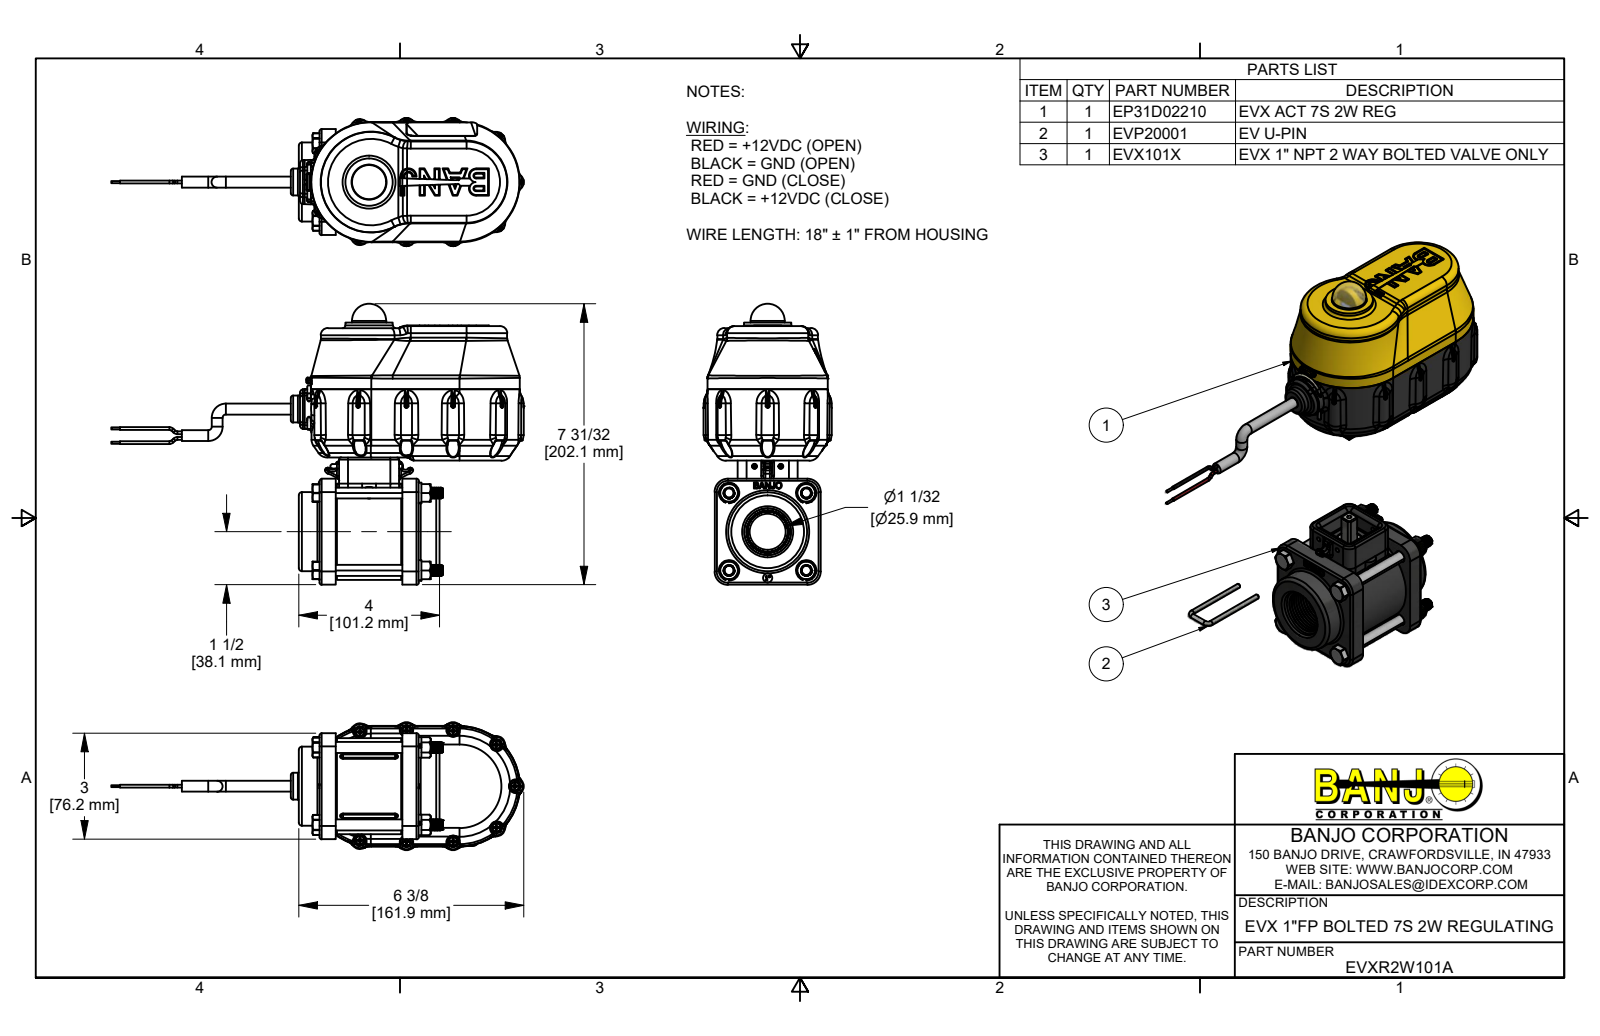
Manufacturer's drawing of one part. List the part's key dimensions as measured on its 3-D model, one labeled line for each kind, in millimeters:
Part name (STEP PRODUCT): EVXR2W101A; EVP20001; EVX101X; MEVX10254A (+8 more)
STEP written by: Autodesk Inventor 2019 (AUTOMOTIVE_DESIGN)
Units: millimetres
Bodies: 95 solids, 12807 faces (3636 planar, 3423 cylindrical, 5748 other)
Overall size (bounding box): 984.8 × 202.1 × 92.2
Volume: 822 600 mm³ · Surface area: 477 700 mm²
Round holes (diameter × count): ⌀3.8 ×13, ⌀2.4 ×11, ⌀2.7 ×4, ⌀3.2 ×4, ⌀3.4 ×4, ⌀3.5 ×4, ⌀4.3 ×4, ⌀6.4 ×4, ⌀8.2 ×4, ⌀8.9 ×4, ⌀25.9 ×3, ⌀2.3 ×2
Round bosses / shafts (diameter × count): ⌀6.8 ×60, ⌀6.4 ×17, ⌀3.6 ×11, ⌀2.7 ×11, ⌀2.2 ×11, ⌀2 ×10, ⌀8 ×5, ⌀14.8 ×4
Partial cylindrical surfaces — rounded edges, fillets, slot ends (radius × count): R1 ×147, R0.5 ×83, R1.5 ×62, R0.3 ×56, R0.1 ×41, R0.8 ×32, R2 ×28, R2.5 ×22
Main face-to-face distances: 2.5, 65.2, 42.8, 62.6, 19.8, 1.4, 11.7, 3.2, 4.2, 22.4
Hole centre spacings: 55.7, 26.6, 32.6, 39.4, 42.2, 48, 80.9, 83.7
